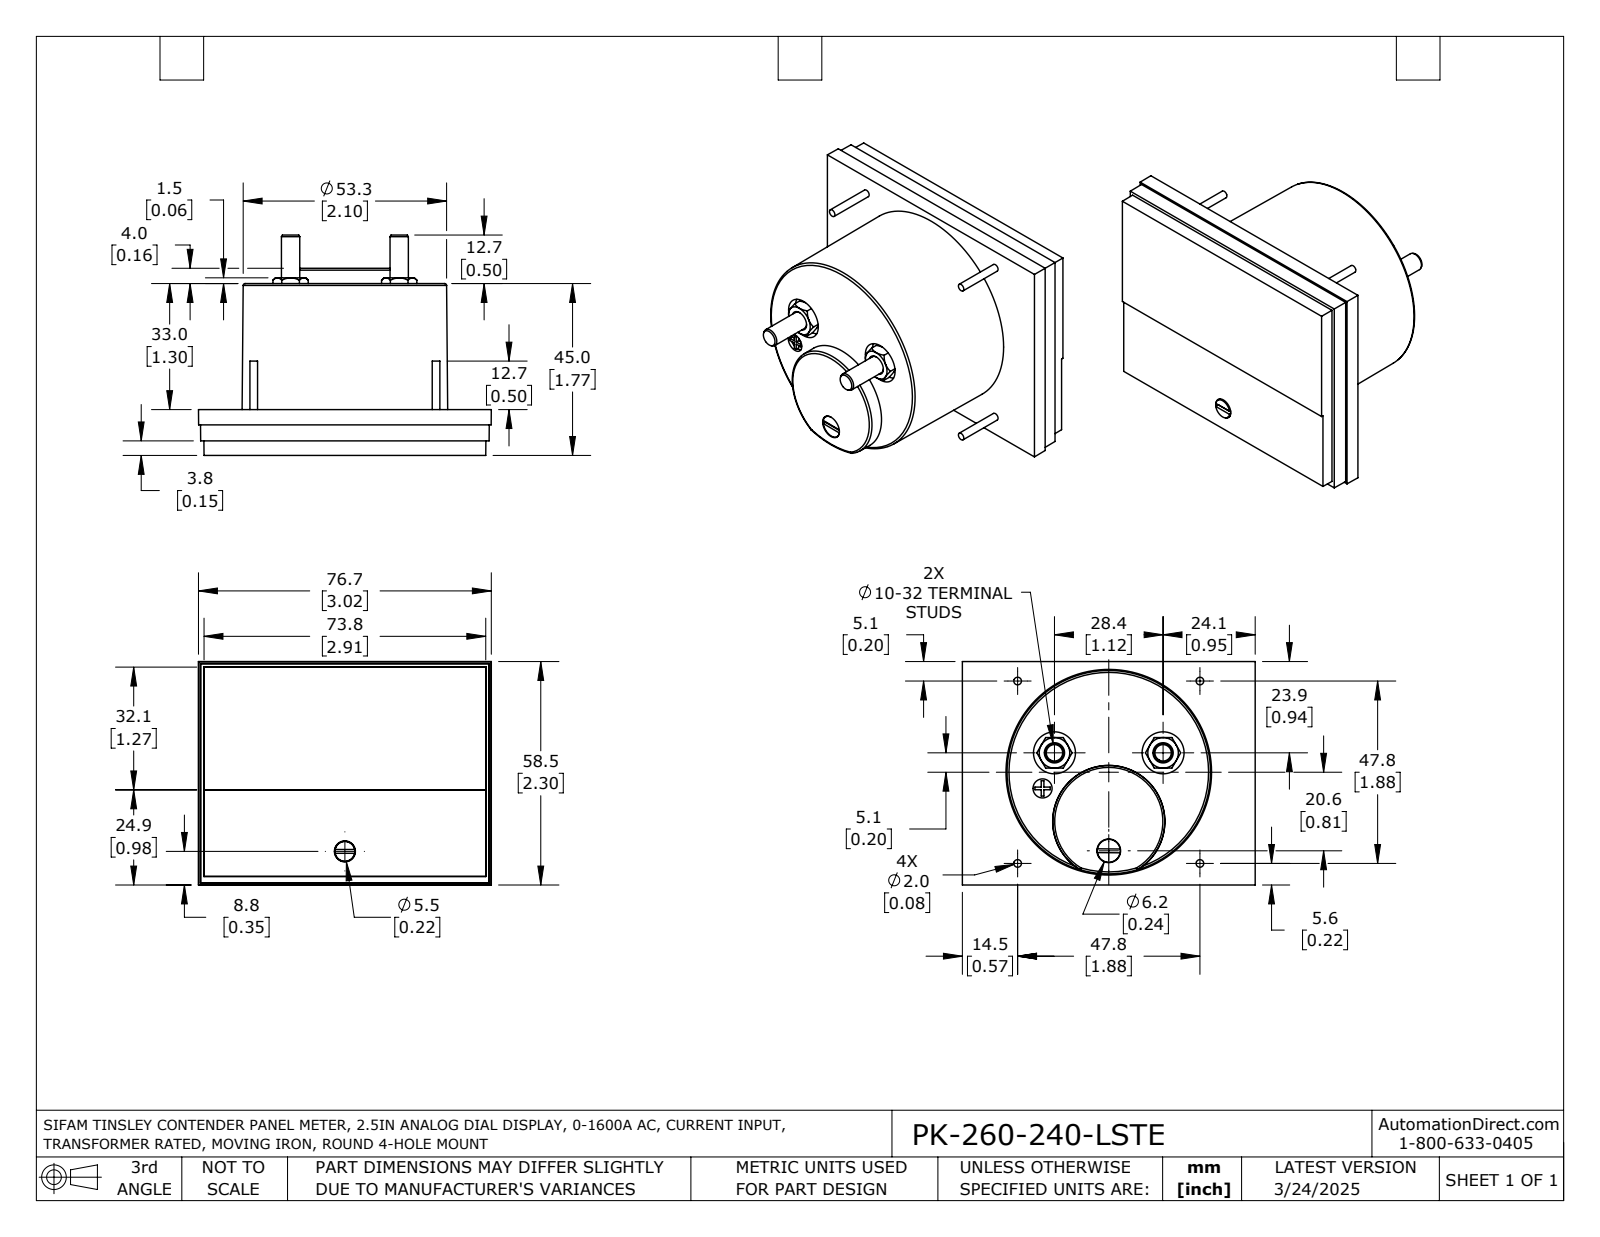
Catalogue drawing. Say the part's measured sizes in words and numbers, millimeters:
The part is named "PK-260-240-LSTE". Its 3-D file was written by "SolidWorks 2021 (AUTOMOTIVE_DESIGN)". It is 1 solid with 192 faces: 95 planar, 37 cylindrical and 60 other. Overall it measures 76.7 by 58.5 by 57.7 millimeters. Its volume is 125 500 cubic millimeters and its surface area 23 580 square millimeters. Round holes: 3 of diameter 5, 2 of diameter 11, 1 of diameter 5.3, 1 of diameter 5.5, 1 of diameter 6.2. Round bosses or shafts: 4 of diameter 2, 2 of diameter 4.8, 1 of diameter 6, 1 of diameter 5.2. Partial cylindrical surfaces (rounded edges, fillets, slot ends): 1 of radius 0.8. The main face-to-face distances are 0.5, 12, 3.3, 8.2, 3.8, 11.5, 1.4, 2, 10.1, 1.9. The hole center spacings are 29.3, 29.5, 9.8, 23.8, 23.9, 28.4, 32.9.
